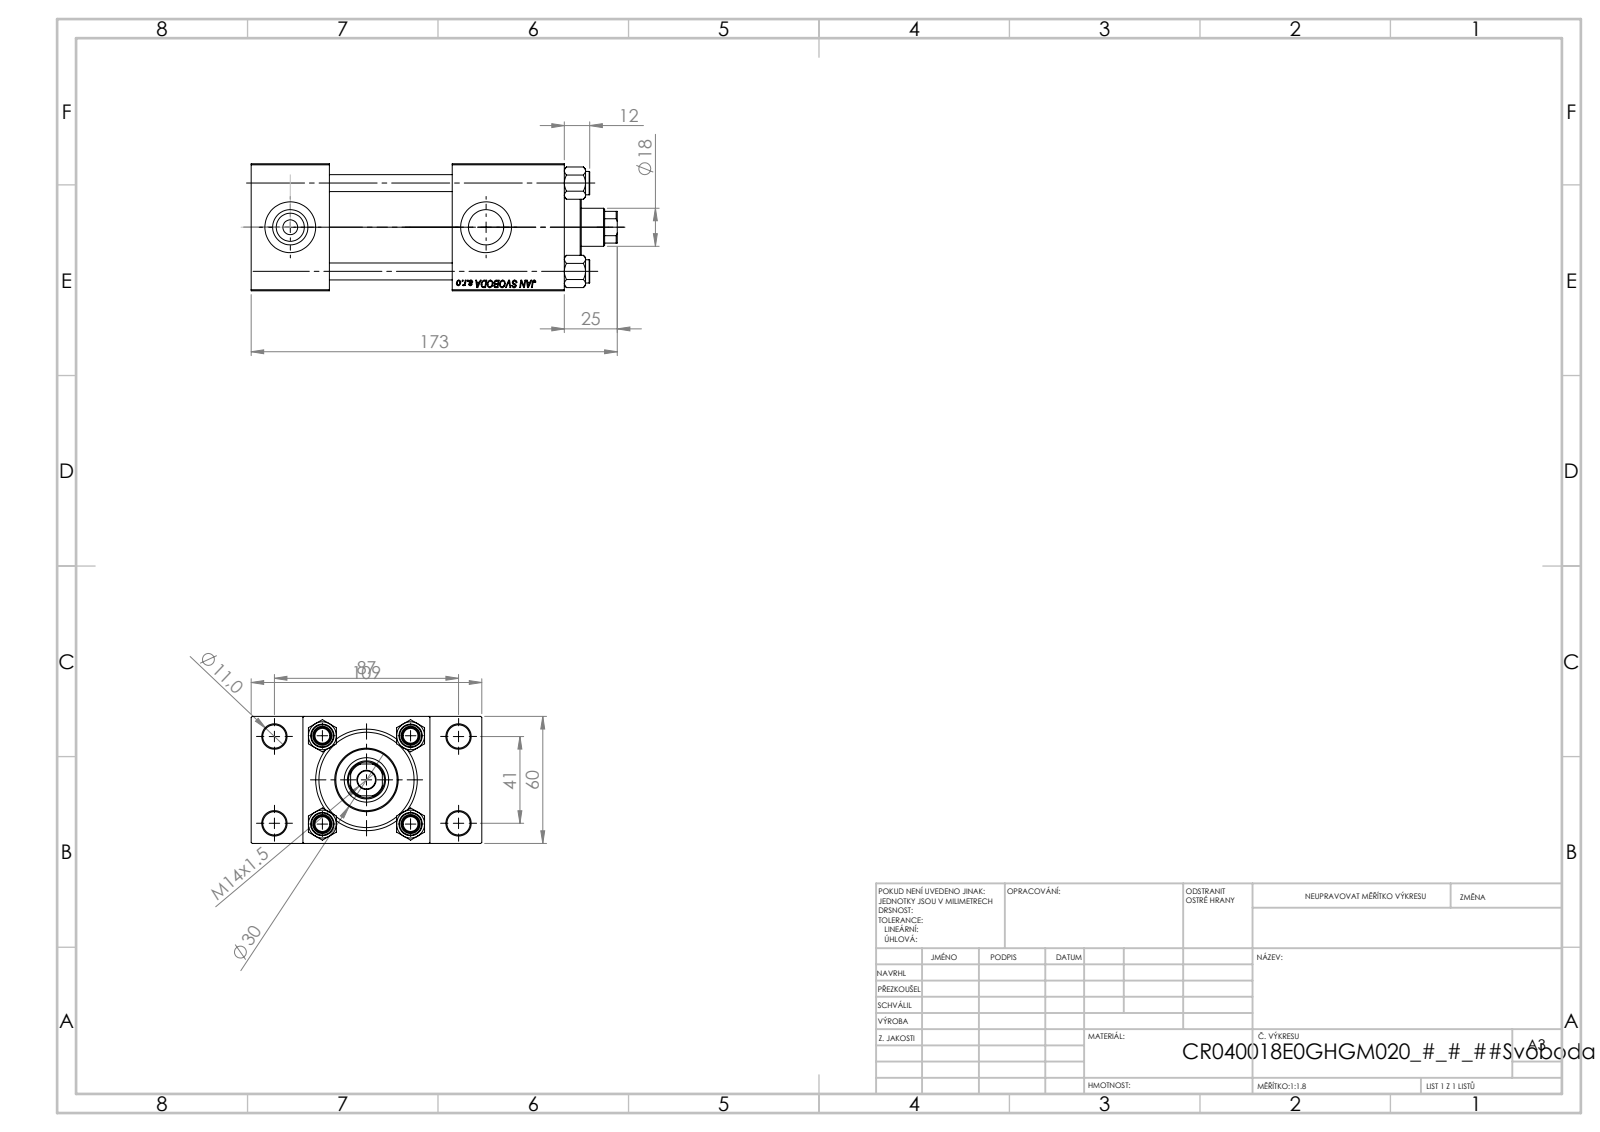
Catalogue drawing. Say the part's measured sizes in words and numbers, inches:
The part is named "V215CR_VCP_E; V215CR_TYCINKA_E; V215CR_E_Body; V215_VC_A (+1 more)". Its 3-D file was written by "SolidWorks 2019 (CONFIG_CONTROL_DESIGN)". It is 11 solids with 1136 faces: 498 planar, 86 cylindrical and 552 other. Overall it measures 6.811 by 4.291 by 2.362 inches. Its volume is 30.48 cubic inches and its surface area 192.9 square inches. Round holes: 4 of diameter 0.315, 4 of diameter 0.433, 2 of diameter 0.276, 2 of diameter 0.656, 2 of diameter 0.945, 1 of diameter 0.335, 1 of diameter 0.709, 1 of diameter 0.827, 1 of diameter 1.22, 1 of diameter 1.575, 1 of diameter 1.772. Round bosses or shafts: 4 of diameter 0.433, 1 of diameter 1.811, 1 of diameter 1.181. Partial cylindrical surfaces (rounded edges, fillets, slot ends): 1 of radius 0.335. The main face-to-face distances are 2.362, 1.457, 0.965, 3.327, 5.827, 4.37, 0.957, 2.283, 2.087, 3.24. The hole center spacings are 0.892, 1.161, 1.642, 1.856, 1.893, 2.533, 3.011, 1.614.
